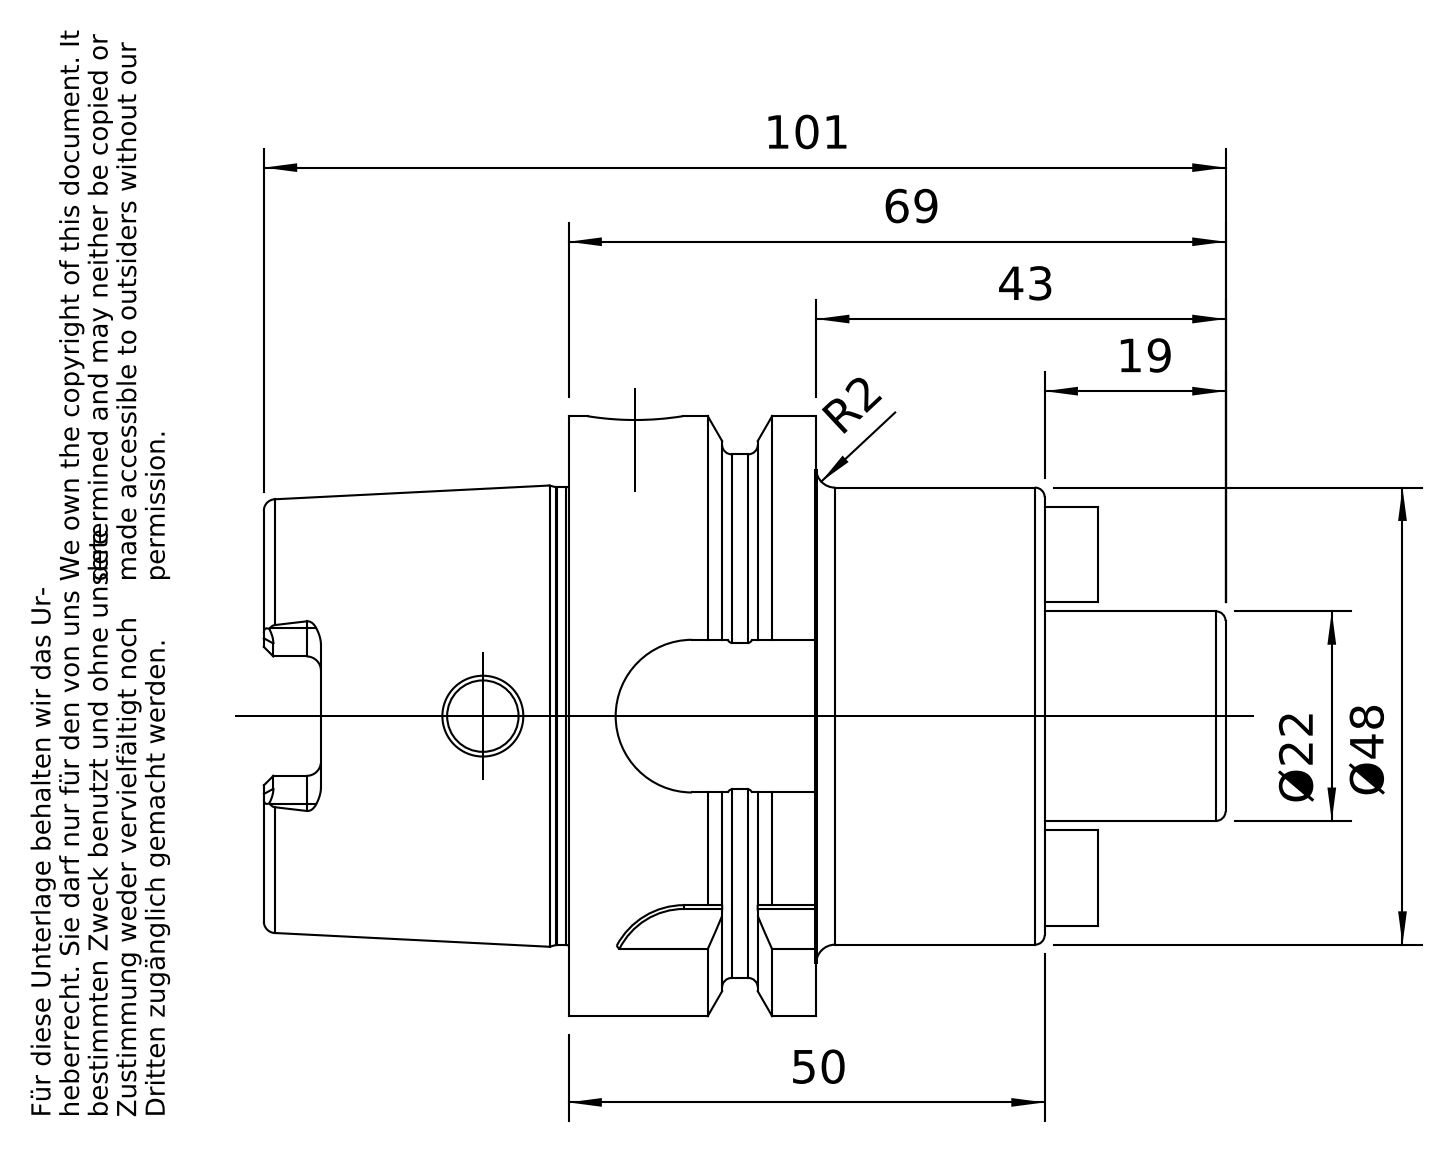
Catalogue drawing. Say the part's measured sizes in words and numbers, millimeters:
The part is named "A63-050-22". Its 3-D file was written by "PRO/ENGINEER BY PARAMETRIC TECHNOLOGY CORPORATION, 2010430 (CONFIG_CONTROL_DESIGN)". It is 1 solid with 190 faces: 68 planar, 52 cylindrical and 70 other. Overall it measures 101 by 63 by 63 millimeters. Its volume is 131 720 cubic millimeters and its surface area 29 317 square millimeters. Round holes: 2 of diameter 10, 1 of diameter 7.5, 1 of diameter 8.5, 1 of diameter 16.92, 1 of diameter 18.32, 1 of diameter 18.66, 1 of diameter 34, 1 of diameter 40. Round bosses or shafts: 1 of diameter 63, 1 of diameter 55, 1 of diameter 48.04, 1 of diameter 48, 1 of diameter 22, 1 of diameter 18. Partial cylindrical surfaces (rounded edges, fillets, slot ends): 6 of radius 1.5, 4 of radius 3, 1 of radius 8, 1 of radius 8.02, 1 of radius 9.02. The main face-to-face distances are 50, 26, 24, 10, 16, 40, 32, 42, 58, 82.
